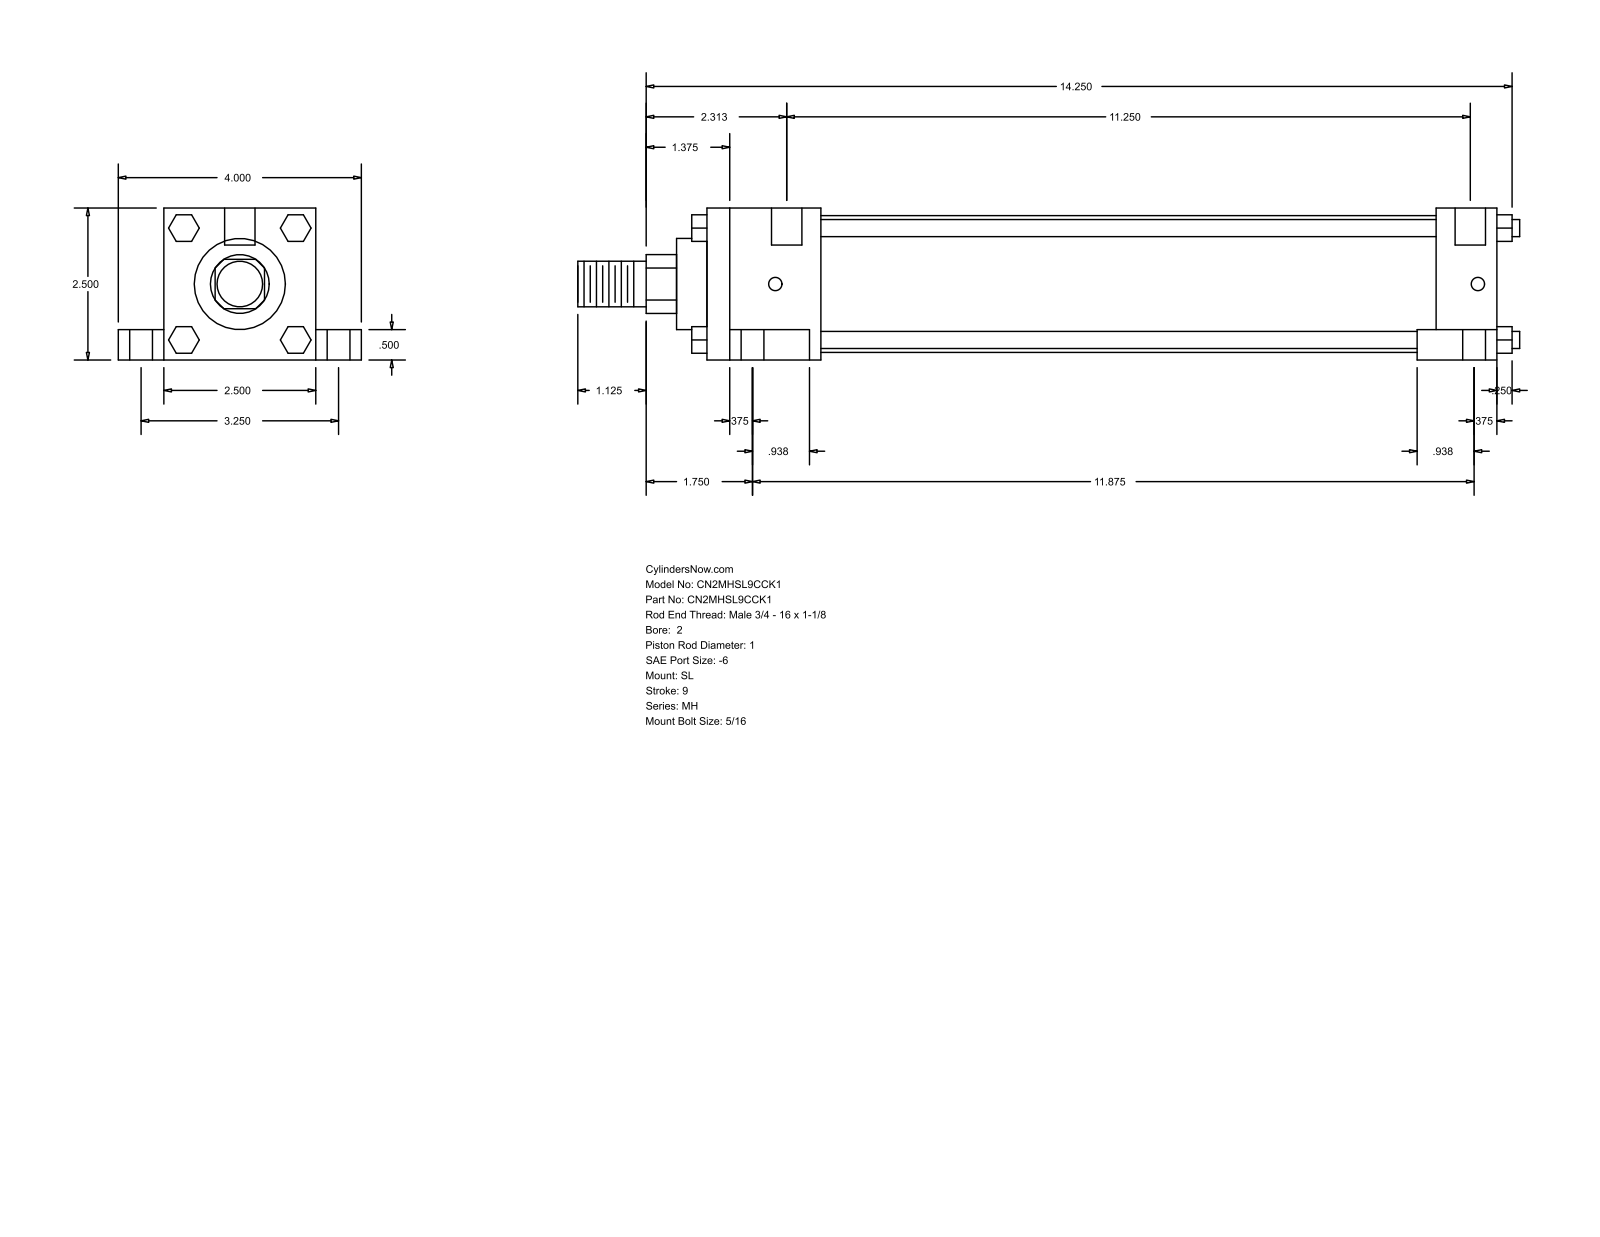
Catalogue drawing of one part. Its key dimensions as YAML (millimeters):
part_name: "MH_SL__0200_1"
step_written_by: "GSSL Pune (CONFIG_CONTROL_DESIGN)"
units: millimeters
bodies: {solids: 0, faces: 148, planar: 112, cylindrical: 36, other: 0}
overall_size: [393.7, 101.6, 63.5]
round_holes:
  - {diameter: 5.56, count: 4}
  - {diameter: 9.53, count: 4}
  - {diameter: 15.88, count: 4}
  - {diameter: 12.7, count: 2}
round_bosses_or_shafts:
  - {diameter: 7.14, count: 4}
  - {diameter: 57.15, count: 1}
  - {diameter: 38.1, count: 1}
  - {diameter: 25.4, count: 1}
  - {diameter: 19.05, count: 1}
partial_cylinders:
  - {radius: 12.29, count: 1}
face_to_face_distances: [63.5, 330.2, 12.7, 19.05, 50.8, 82.55, 25.4, 304.8, 47.63, 257.17]
hole_center_spacings: [41.3, 42.36, 43.67, 82.54, 290.28, 293.68, 294.99, 301.62]
